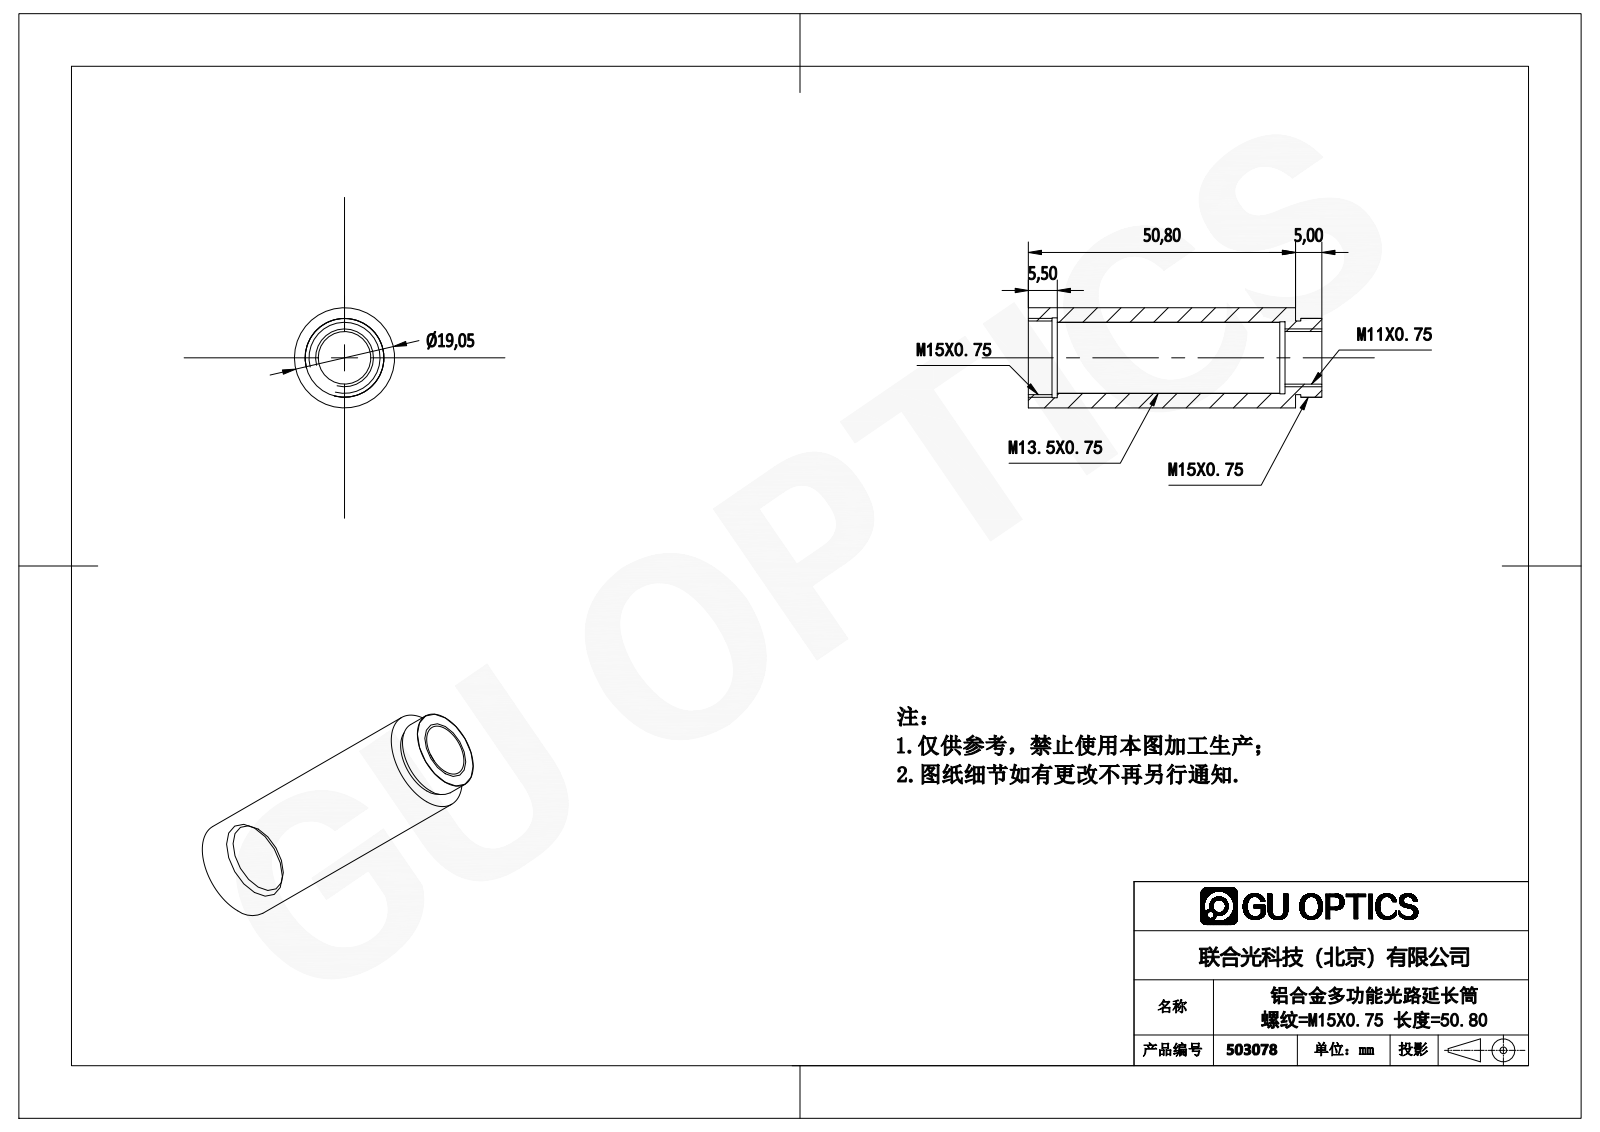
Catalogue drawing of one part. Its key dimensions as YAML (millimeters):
part_name: "503078"
step_written_by: "SolidWorks 2016 (AUTOMOTIVE_DESIGN)"
units: millimeters
bodies: {solids: 1, faces: 24, planar: 8, cylindrical: 16, other: 0}
overall_size: [55.8, 19.05, 19.05]
volume: 7714
surface_area: 6097
round_holes:
  - {diameter: 10, count: 1}
  - {diameter: 13.5, count: 1}
  - {diameter: 13.7, count: 1}
  - {diameter: 14, count: 1}
  - {diameter: 15.2, count: 1}
round_bosses_or_shafts:
  - {diameter: 19.05, count: 1}
  - {diameter: 15, count: 1}
face_to_face_distances: [50.8, 55.8, 5, 48.8, 2, 7, 1, 46.3, 43.3, 5.5]
